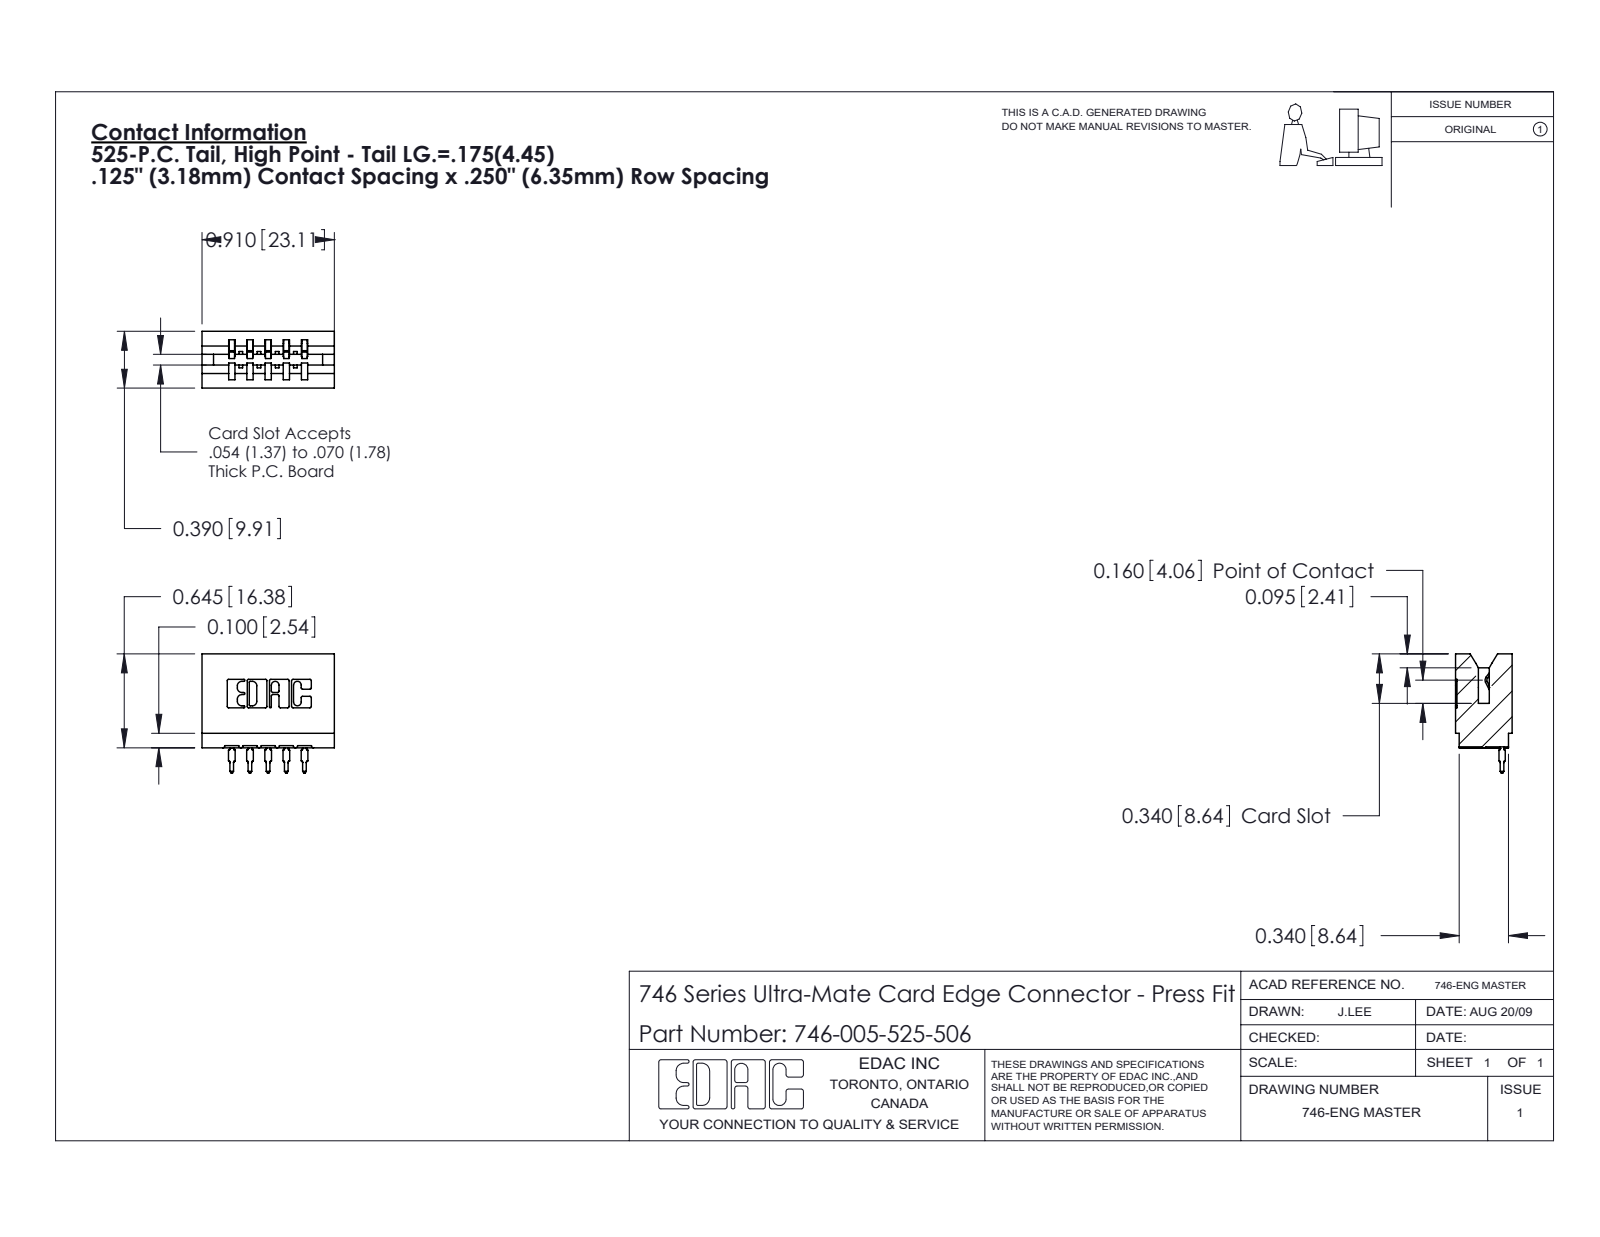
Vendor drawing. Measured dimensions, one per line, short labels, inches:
name: 746 Part_.340 Slot Depth - 06; 746-292-001_525; 746-005-525-506
written by: SolidWorks 2020 (CONFIG_CONTROL_DESIGN)
unit: in
bodies: 6 solids, 638 faces (371 planar, 137 cylindrical, 130 other)
size: 0.91 × 0.819 × 0.39
volume: 0.17 in³; area: 4.94 in²
rounds: 22× R0.01, 10× R0.021, 6× R0.007, 6× R0.015, 6× R0.031, 4× R0.005, 4× R0.011, 3× R0.026
face distances: 0.25, 0.042, 0.125, 0.125, 0.333, 0.057, 0.39, 0.292, 0.208, 0.083
